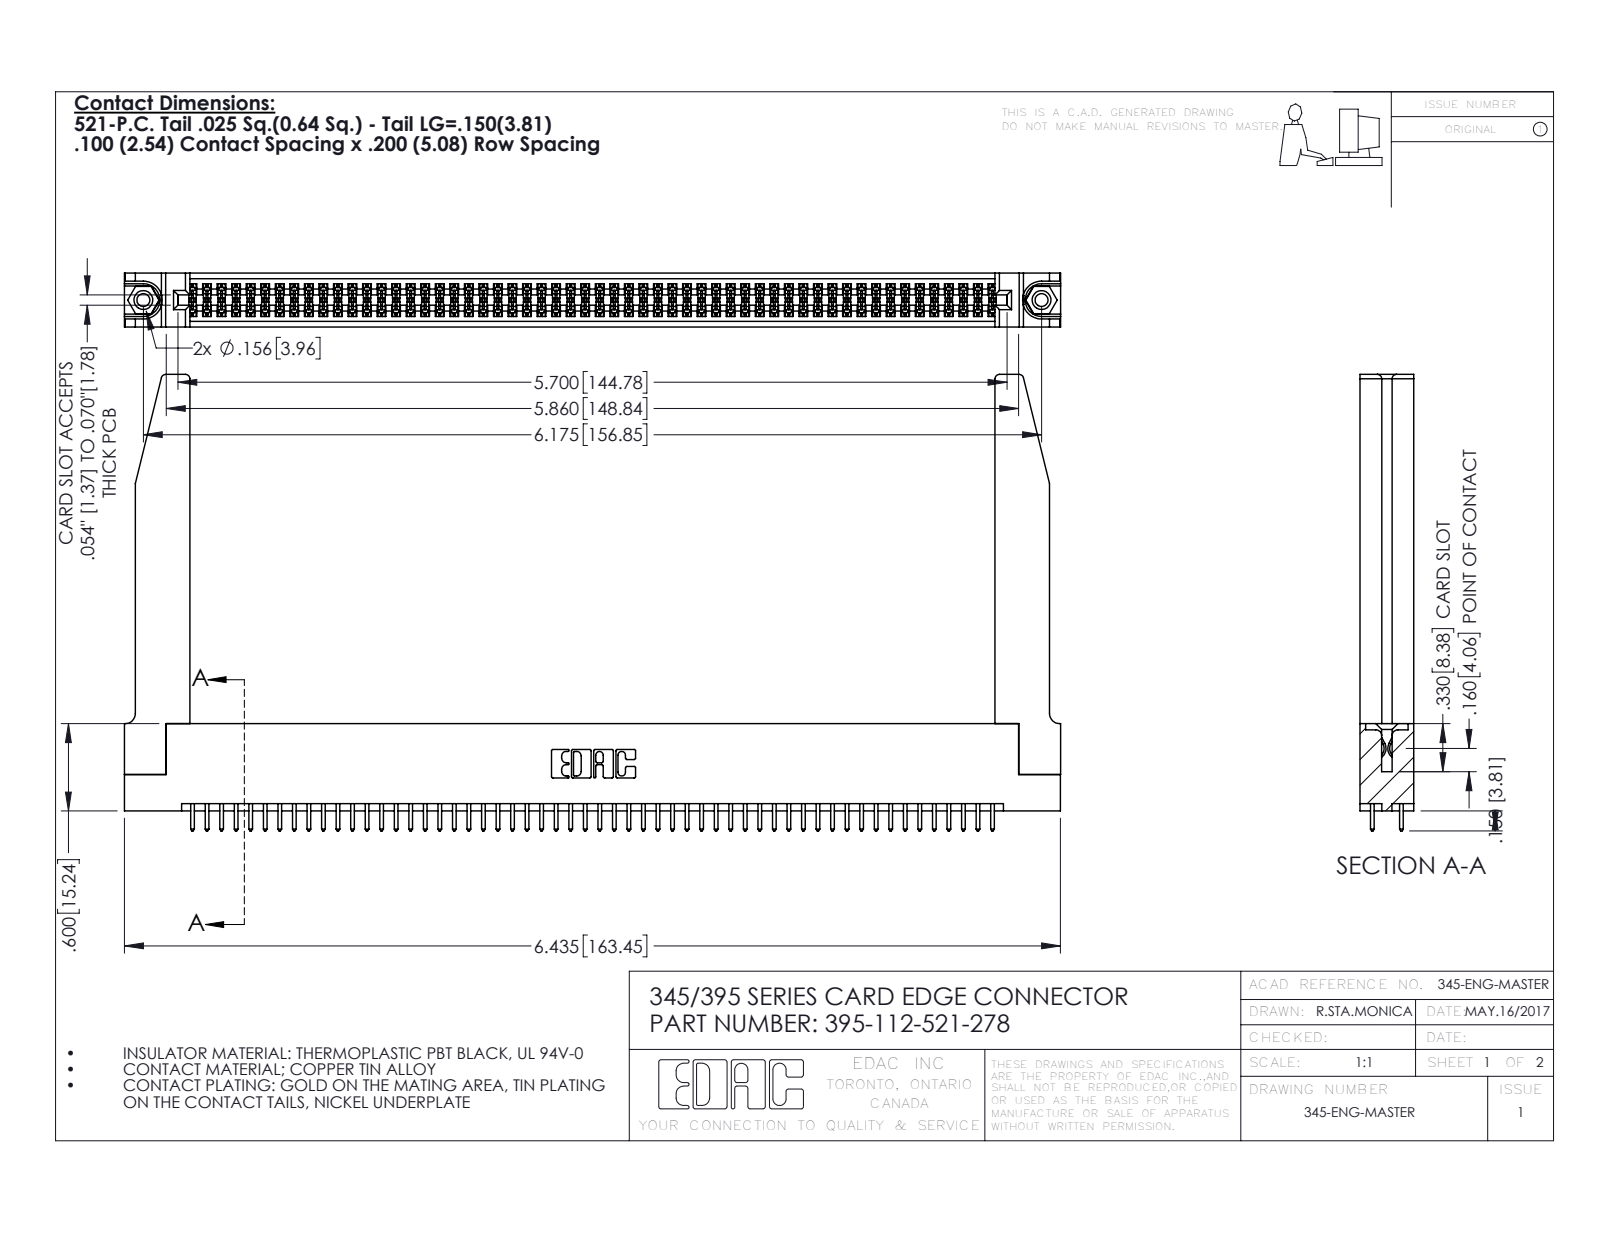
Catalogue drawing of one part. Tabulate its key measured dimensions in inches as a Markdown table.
| quantity | value |
| --- | --- |
| part name | 395-112-521-278; 345 Part_Flush Mounting Lugs - 0.156 Dia-TH; 345-220-078_345-220-078; 345-292-001_345-293-121 (+1 more) |
| STEP written by | SolidWorks 2016 (CONFIG_CONTROL_DESIGN) |
| units | inches |
| bodies | 117 solids, 5960 faces (3918 planar, 1990 cylindrical, 52 other) |
| overall size | 6.436 × 3.137 × 0.37 |
| volume | 1.448 in³ |
| surface area | 47.14 in² |
| round holes (diameter × count) | 0.089 × 2, 0.125 × 2, 0.156 × 2, 0.064 × 1 |
| round bosses / shafts (diameter × count) | 0.155 × 2 |
| partial cylindrical surfaces (radius × count) | 0.006 × 168, 0.01 × 112, 0.01 × 22, 0.03 × 8, 0.007 × 6, 0.031 × 6, 0.026 × 3, 0.014 × 2 |
| main face-to-face distances | 0.072, 0.298, 0.37, 0.2, 0.098, 0.272, 0.025, 0.225, 0.175, 0.148 |
| hole center spacings | 0.27, 5.939, 6.175 |
